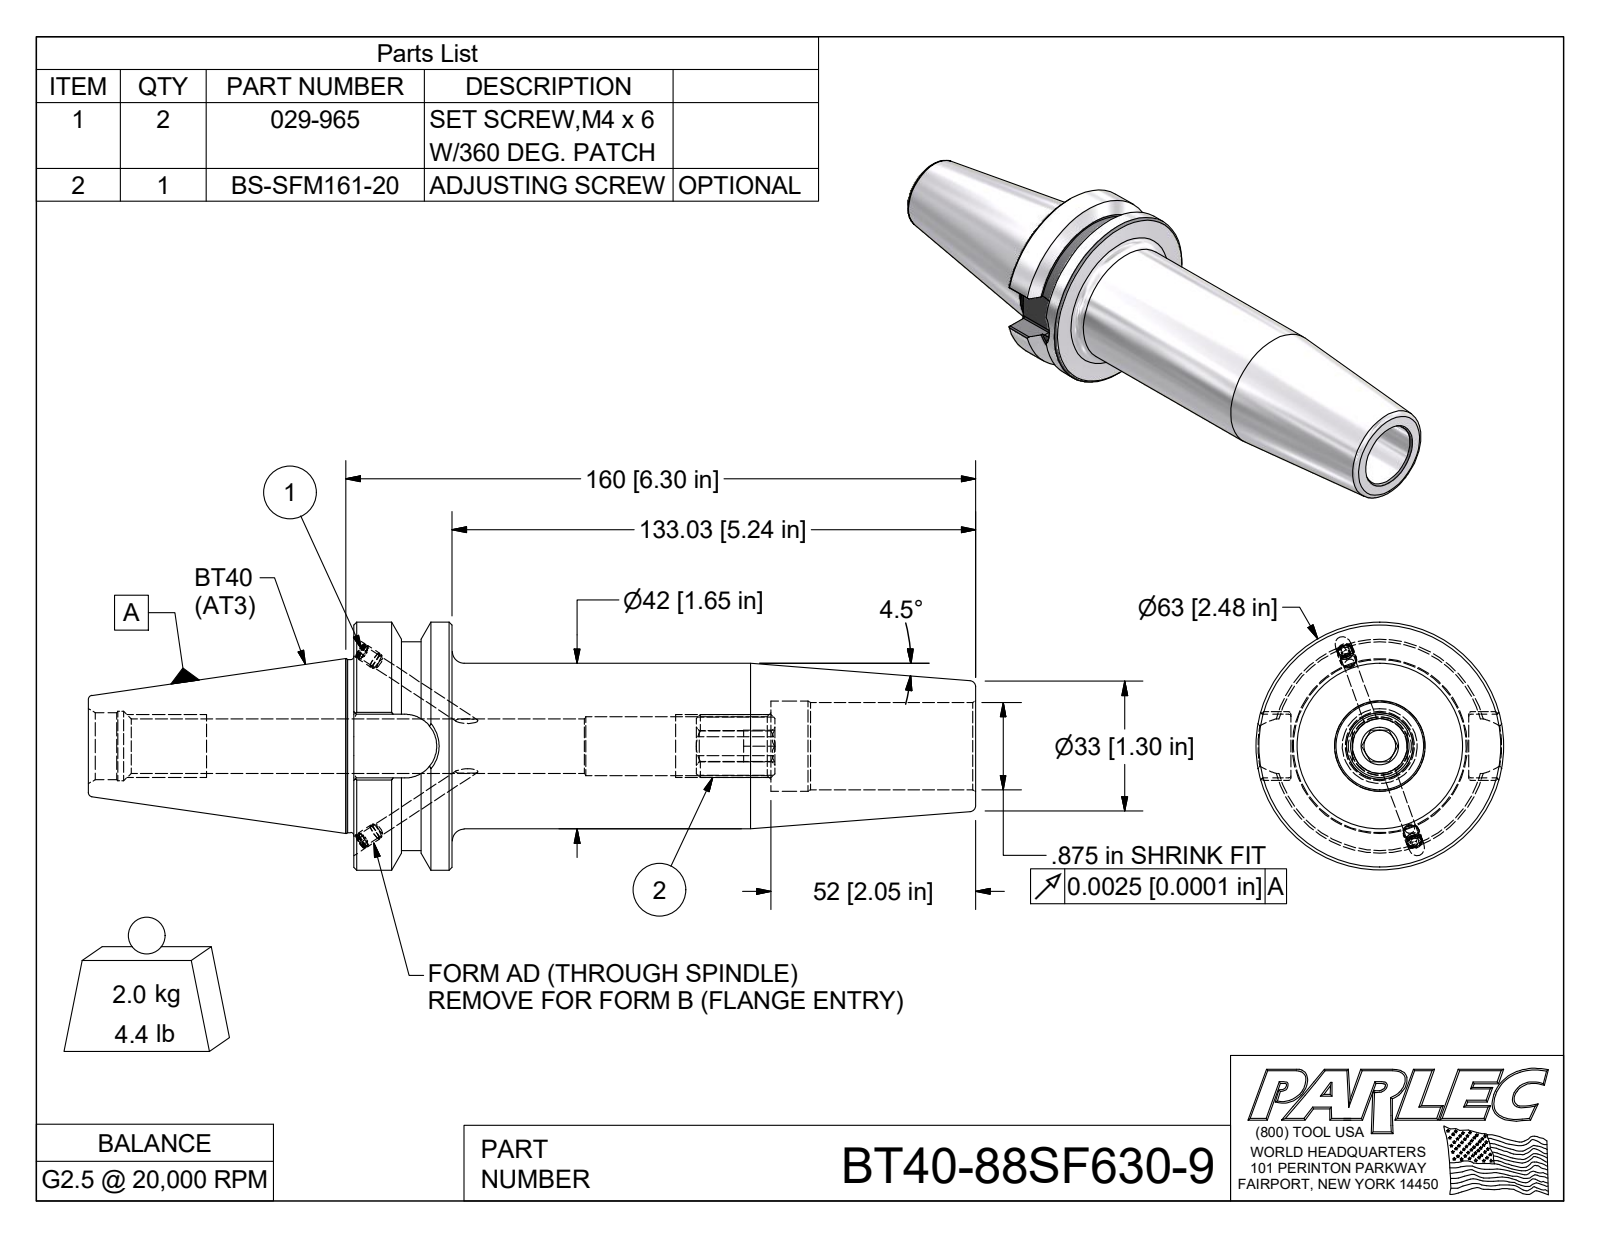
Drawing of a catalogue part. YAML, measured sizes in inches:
part_name: "BT40-88SF630-9; BT40BC-88SF630-9-1; 029-965; BS-SFM161-20"
step_written_by: "Autodesk Inventor 2009 (AUTOMOTIVE_DESIGN)"
units: inches
bodies: {solids: 4, faces: 131, planar: 57, cylindrical: 33, other: 41}
overall_size: [8.874, 2.48, 2.48]
volume: 15.99
surface_area: 73.96
round_holes:
  - {diameter: 0.13, count: 2}
  - {diameter: 0.161, count: 2}
  - {diameter: 0.694, count: 1}
  - {diameter: 0.749, count: 1}
  - {diameter: 0.779, count: 1}
round_bosses_or_shafts:
  - {diameter: 0.165, count: 2}
  - {diameter: 0.157, count: 2}
  - {diameter: 2.48, count: 1}
  - {diameter: 2.087, count: 1}
  - {diameter: 1.75, count: 1}
  - {diameter: 1.73, count: 1}
  - {diameter: 1.654, count: 1}
partial_cylinders:
  - {radius: 0.02, count: 8}
  - {radius: 0.315, count: 1}
  - {radius: 0.319, count: 1}
face_to_face_distances: [0.984, 6.221, 5.237, 0.615, 1.166, 1.78, 2.653, 3.637, 8.874, 0.551]
